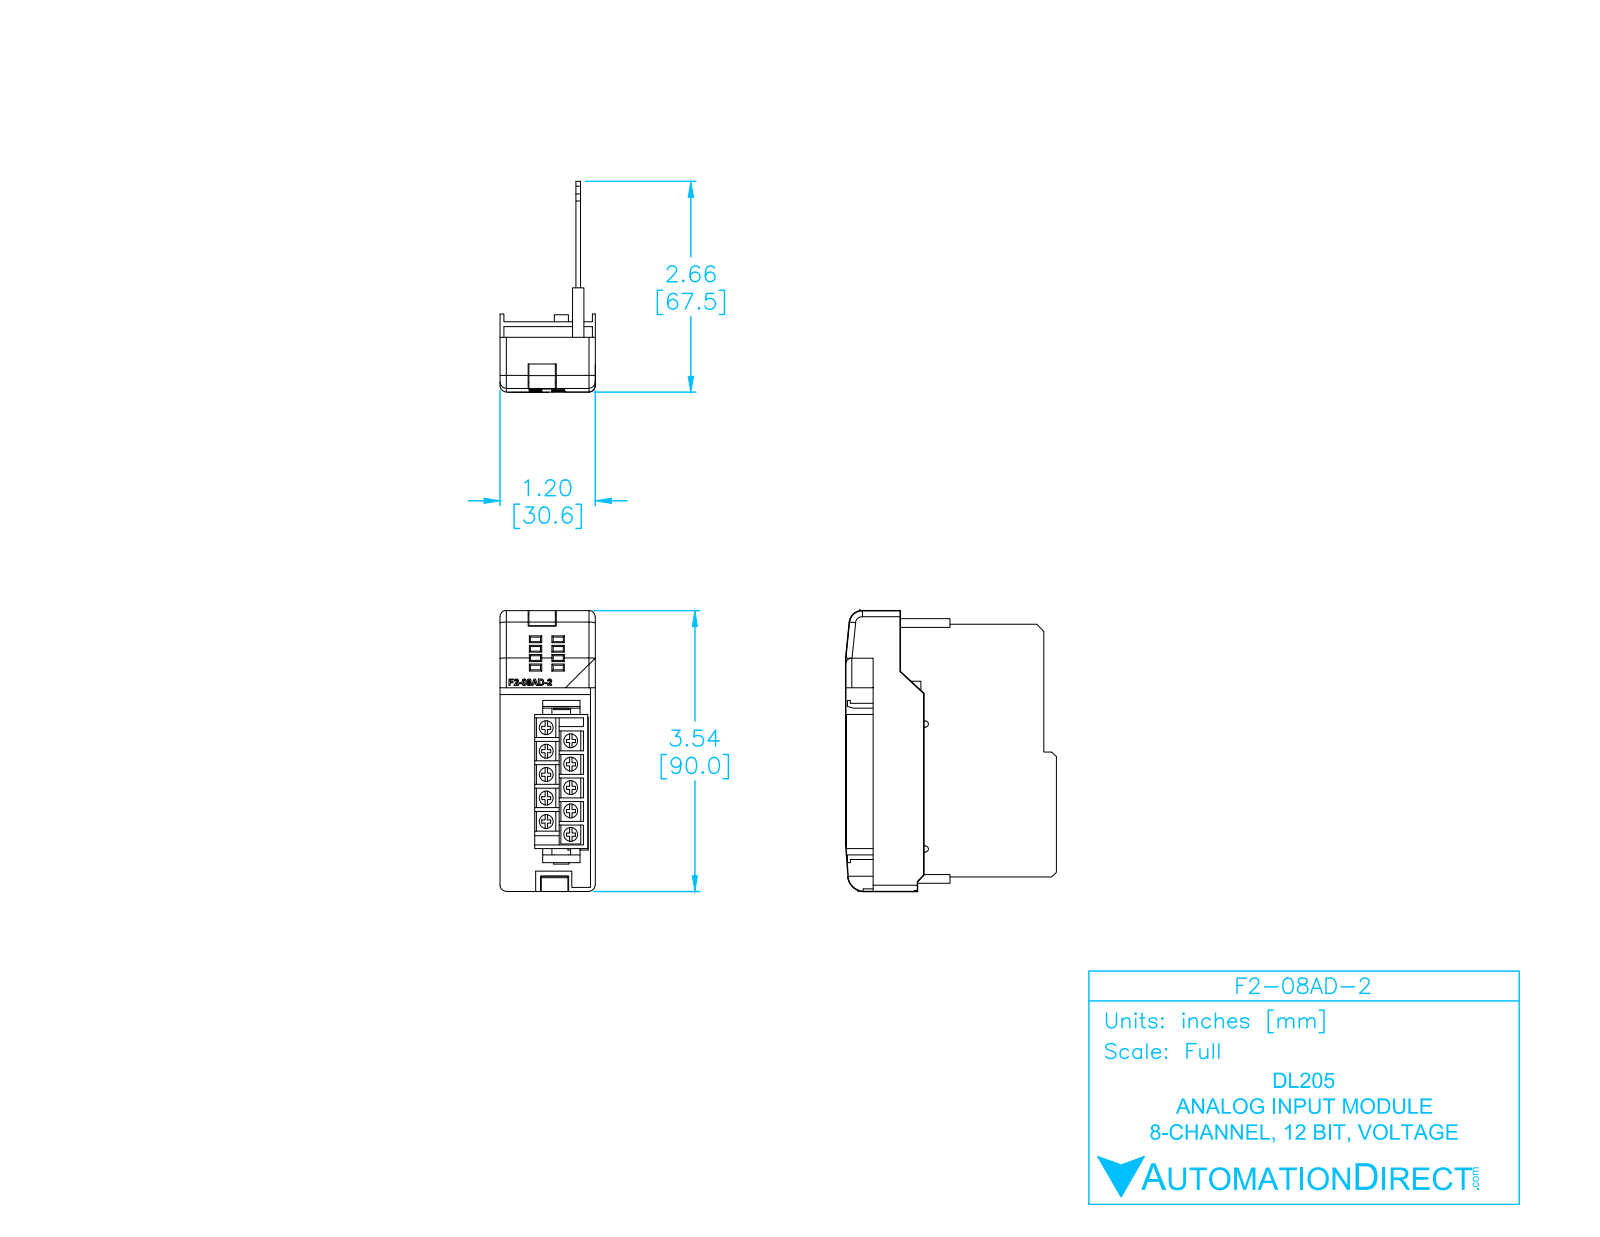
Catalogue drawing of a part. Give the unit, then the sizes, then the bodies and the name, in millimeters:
Units: millimetres
Overall size (bounding box): 90 × 67.61 × 30.55
Round bosses / shafts (diameter × count): ⌀4.5 ×10
Partial cylindrical surfaces — rounded edges, fillets, slot ends (radius × count): R0.35 ×16, R2 ×9, R0.25 ×2, R1 ×2, R1.25 ×2, R4.12 ×1, R5.39 ×1
Main face-to-face distances: 1.5, 4.72, 6.22, 3.62, 2.12, 2.6, 3.22, 1.1, 8.14, 24.28
Volume: 25 374 mm³ · Surface area: 28 533 mm²
Bodies: 6 solids, 586 faces (411 planar, 75 cylindrical, 100 other)
Part name (STEP PRODUCT): F2-08AD-2_ModuleCase_light_NEW
STEP written by: SolidWorks 2009 (AUTOMOTIVE_DESIGN)
